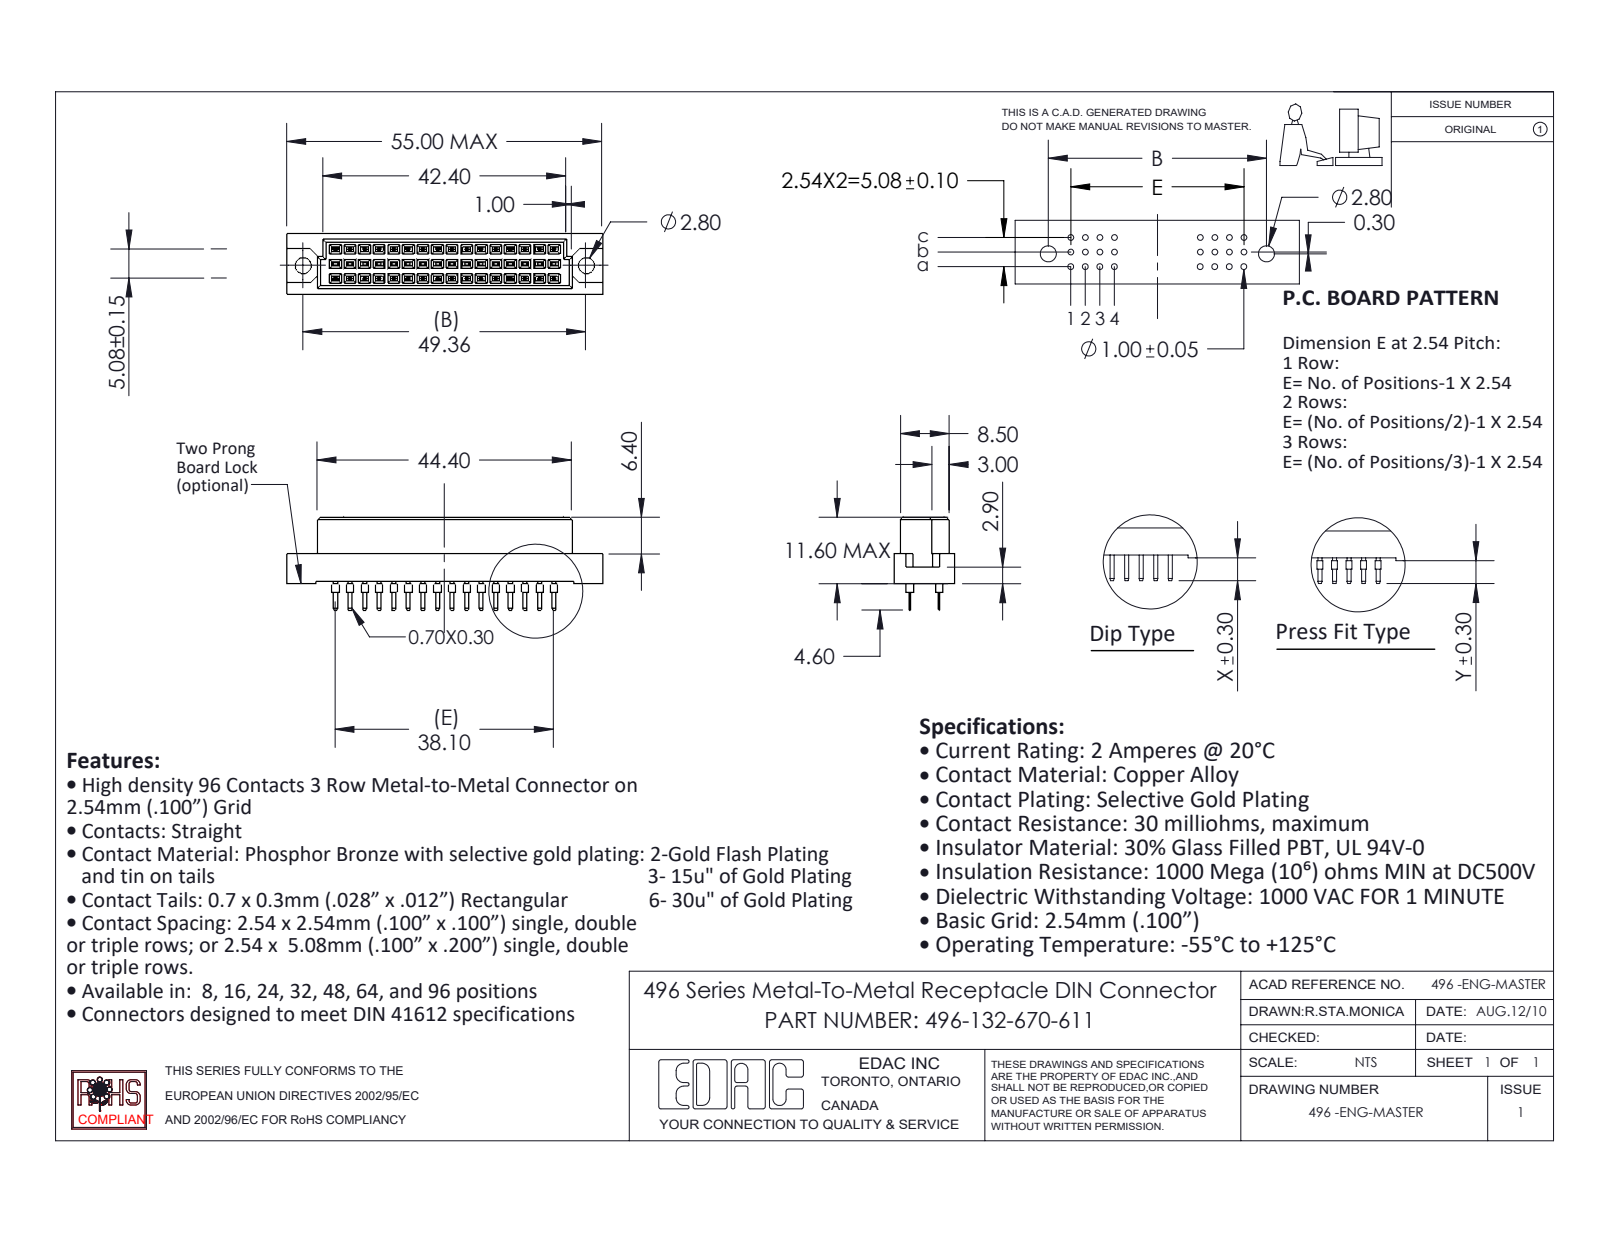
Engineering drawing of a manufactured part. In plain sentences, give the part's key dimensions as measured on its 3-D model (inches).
The part is named "496-132-670-611; 496 Part_48; 496-290_70". Its 3-D file was written by "SolidWorks 2020 (CONFIG_CONTROL_DESIGN)". It is 33 solids with 1242 faces: 1174 planar, 68 cylindrical and 0 other. Overall it measures 2.165 by 0.638 by 0.417 inches. Its volume is 0.285 cubic inches and its surface area 7.561 square inches. Round holes: 2 of diameter 0.11. Round bosses or shafts: 32 of diameter 0.039. The main face-to-face distances are 0.1, 0.2, 0.041, 0.376, 0.032, 0.022, 0.022, 0.417, 0.103, 0.115. The hole center spacings are 1.943.
